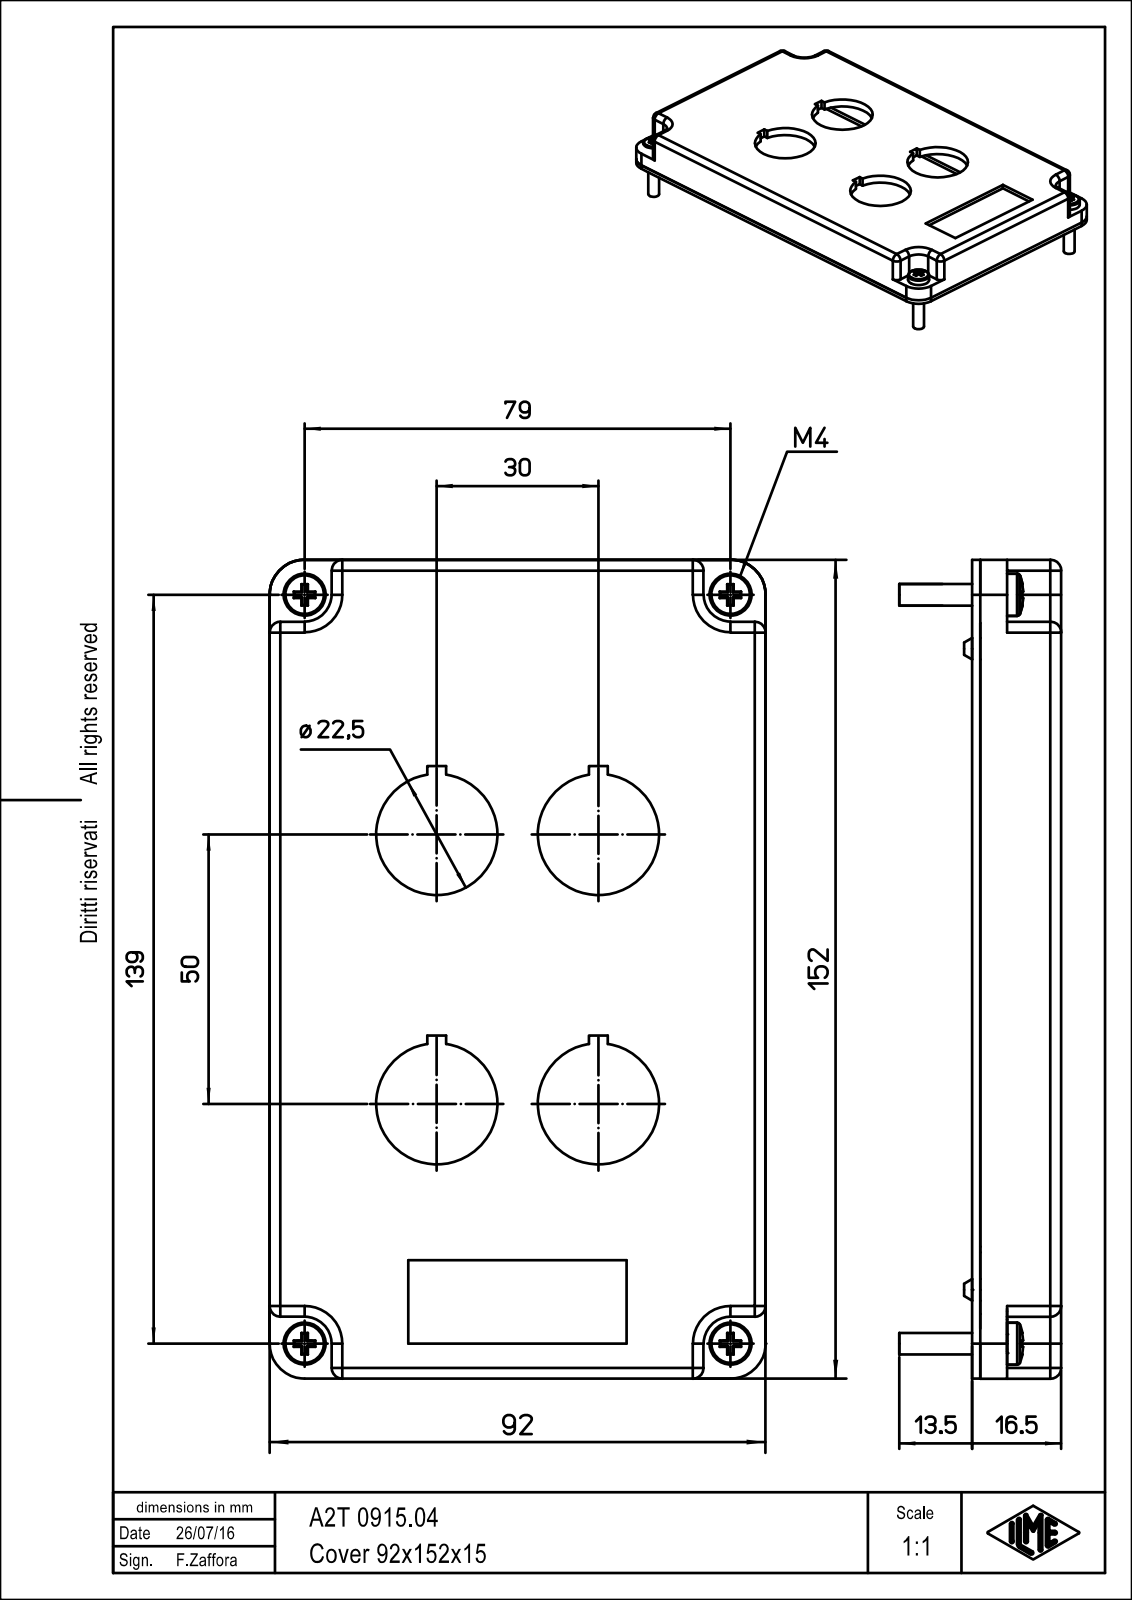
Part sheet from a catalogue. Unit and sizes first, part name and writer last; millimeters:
Units: millimetres
Overall size (bounding box): 152 × 92.02 × 30
Round holes (diameter × count): ⌀4.5 ×4, ⌀22.5 ×4, ⌀3.3 ×1, ⌀5.8 ×1
Round bosses / shafts (diameter × count): ⌀7.8 ×4, ⌀4 ×4, ⌀6 ×2, ⌀7 ×1, ⌀6.2 ×1
Partial cylindrical surfaces — rounded edges, fillets, slot ends (radius × count): R2 ×17, R0.33 ×11, R6.5 ×8, R5 ×6, R8 ×6, R0.27 ×2, R0.27 ×2, R0.17 ×1
Main face-to-face distances: 3, 13.5, 16.5, 1.5, 15, 12, 89, 92, 149, 86
Hole centre spacings: 50.8, 70.36, 97.62, 109.09, 30, 50, 58.31, 79
Volume: 66 364 mm³ · Surface area: 48 074 mm²
Bodies: 1 solid, 582 faces (438 planar, 108 cylindrical, 36 other)
Part name (STEP PRODUCT): A2T_0915.04
STEP written by: PTC Creo Elements/Direct Modeling 19.0B 21-Mar-2015 (C) Parametric Technology GmbH (AUTOMOTIVE_DESIGN)
